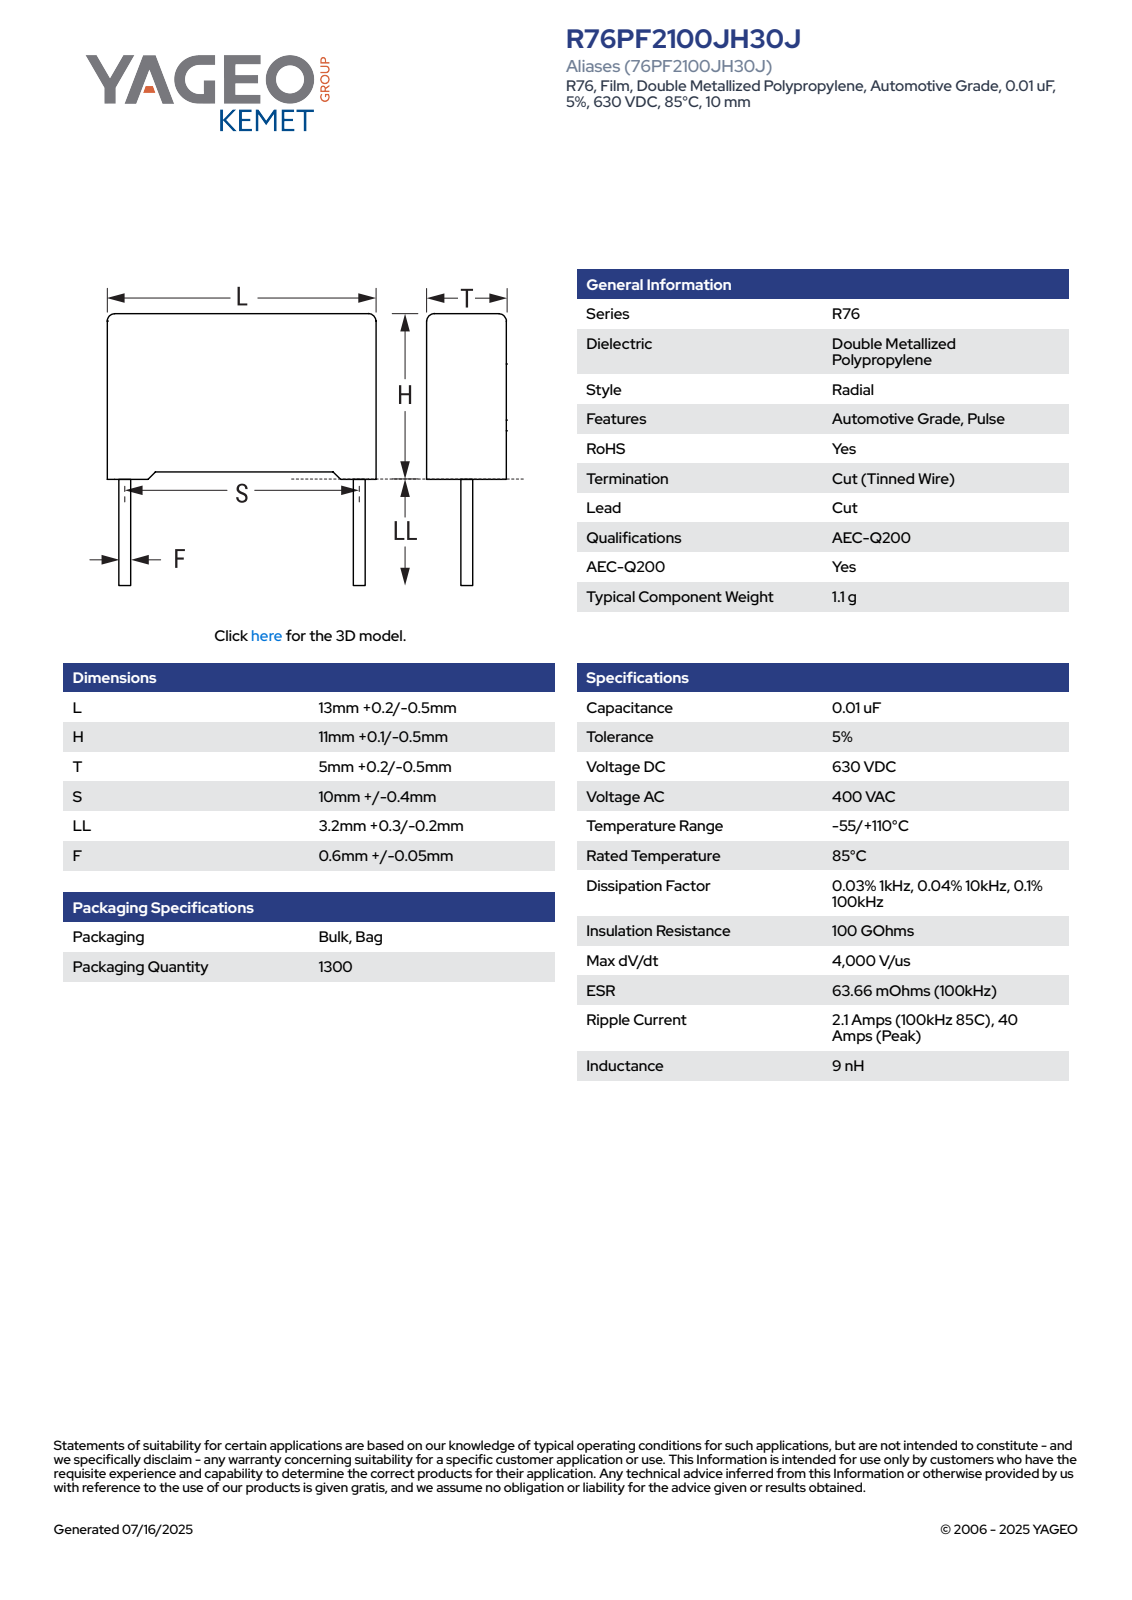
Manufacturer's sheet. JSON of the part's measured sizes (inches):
{"part_name": "CFR_RB2_13X11X5_L13.2H11.1T5.2S10LL3.5F0.65", "step_written_by": "SolidWorks 2021 (AUTOMOTIVE_DESIGN)", "units": "inches", "bodies": {"solids": 4, "faces": 85, "planar": 77, "cylindrical": 8, "other": 0}, "overall_size": [0.575, 0.52, 0.205], "volume_in3": 0.044, "surface_area_in2": 0.904, "round_bosses_or_shafts": [[0.026, 2]], "partial_cylinders_radius": [[0.02, 4]], "face_to_face_distances": [0.205, 0.52, 0.407, 0.017, 0.187, 0.03, 0.437, 0.17, 0.502, 0.015]}
